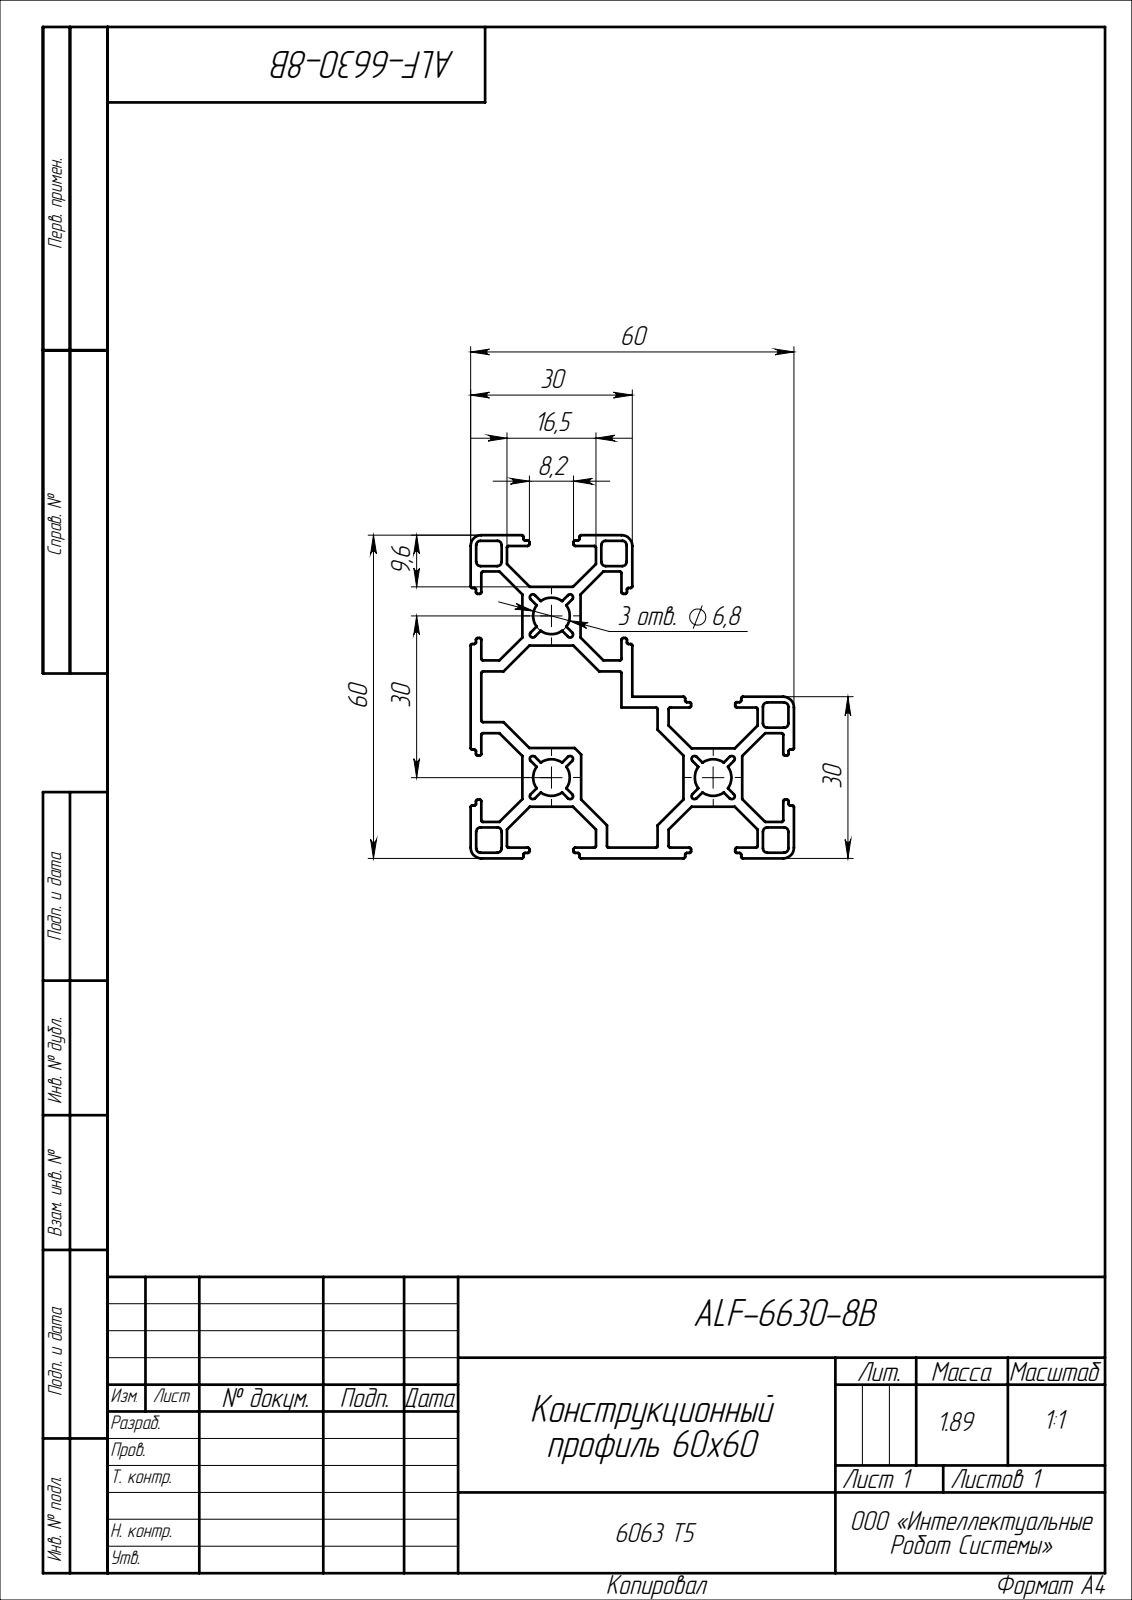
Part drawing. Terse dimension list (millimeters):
name: ALF-6630-8B
written by: SolidWorks 2022 (CONFIG_CONTROL_DESIGN)
unit: mm
bodies: 1 solid, 329 faces (185 planar, 144 cylindrical, 0 other)
size: 1000 × 60 × 60
volume: 701 211 mm³; area: 800 802 mm²
rounds: 86× R0.3, 20× R0.8, 12× R0.55, 5× R2, 3× R3.4
face distances: 2, 30, 28, 9.6, 20.4, 7.6, 21.21, 6.75, 23.25, 50.4
